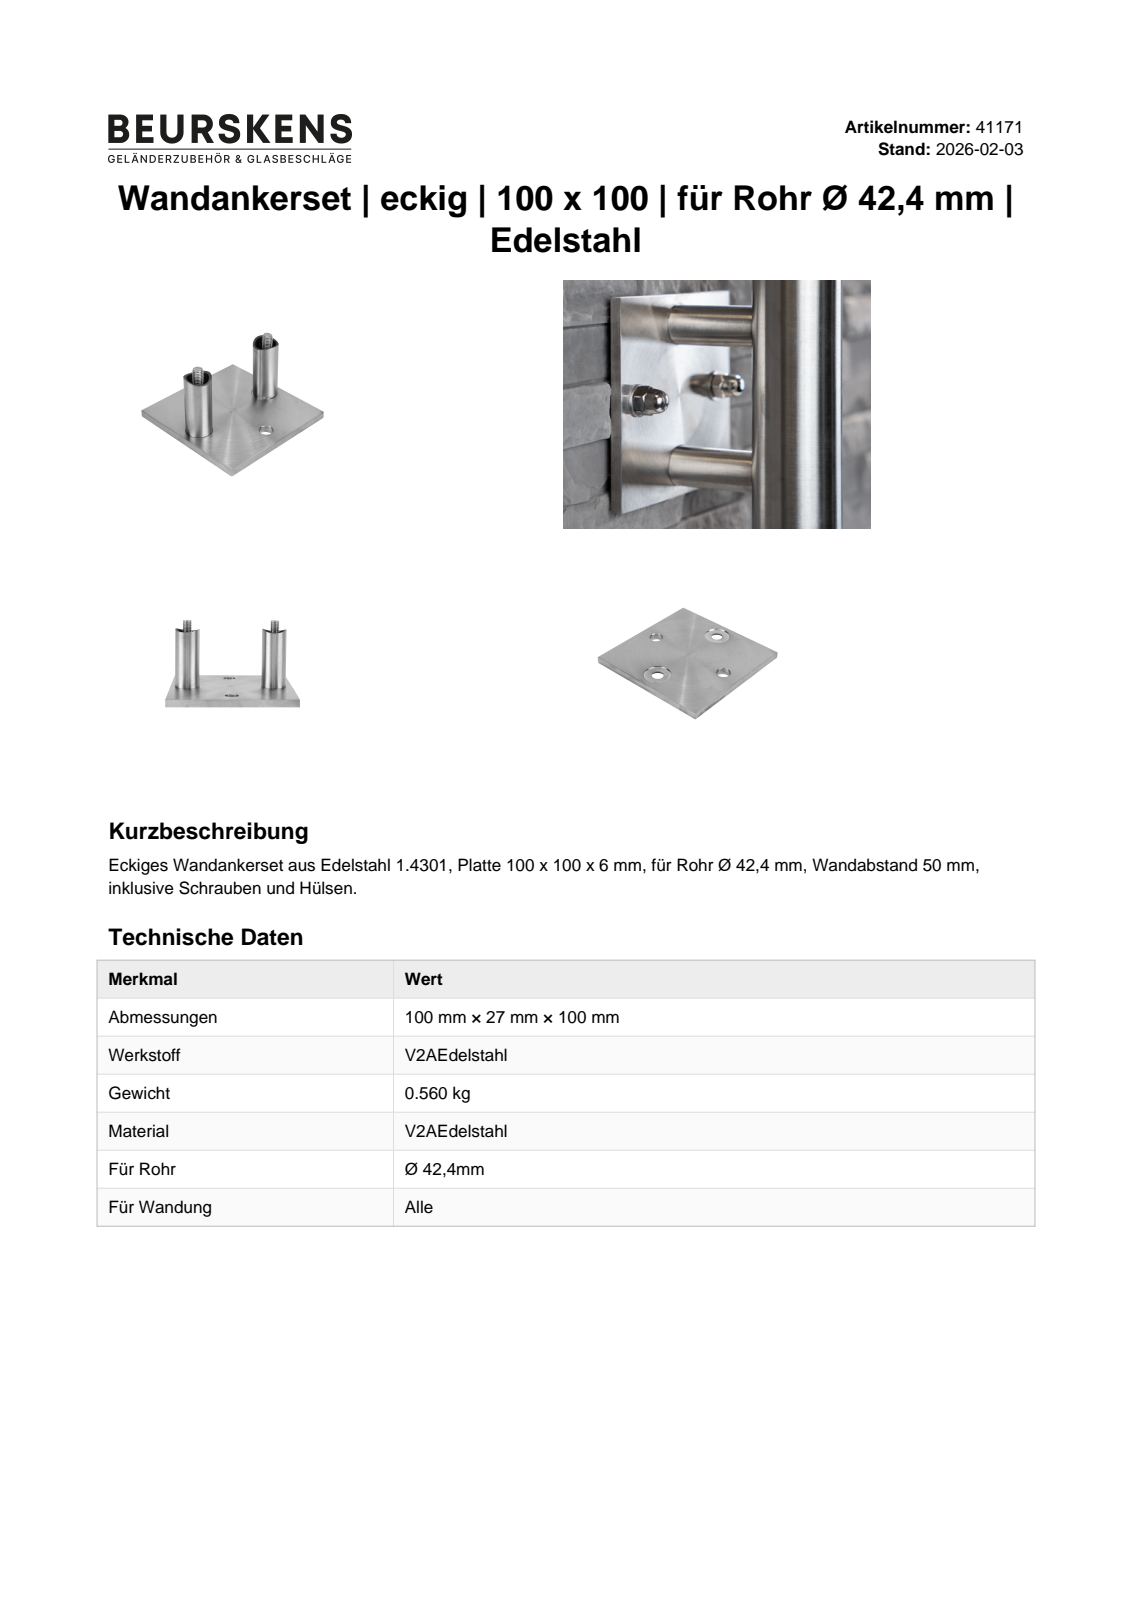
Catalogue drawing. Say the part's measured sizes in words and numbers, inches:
The part is named "41171; 41172; 41141; DIN 7991 - M8 x 60". Its 3-D file was written by "Autodesk Inventor 2022 (AUTOMOTIVE_DESIGN)". It is 5 solids with 50 faces: 26 planar, 16 cylindrical and 8 other. Overall it measures 3.937 by 3.937 by 2.413 inches. Its volume is 4.204 cubic inches and its surface area 58.07 square inches. Round holes: 4 of diameter 0.413, 2 of diameter 0.709, 2 of diameter 0.807. Round bosses or shafts: 2 of diameter 0.787, 2 of diameter 0.6, 2 of diameter 0.315. Partial cylindrical surfaces (rounded edges, fillets, slot ends): 2 of radius 0.835. The main face-to-face distances are 0.236, 3.937, 0.228, 0.051, 0.178, 0.185, 2.413, 2.362, 2.185, 2.177. The hole center spacings are 1.949, 2.756.
